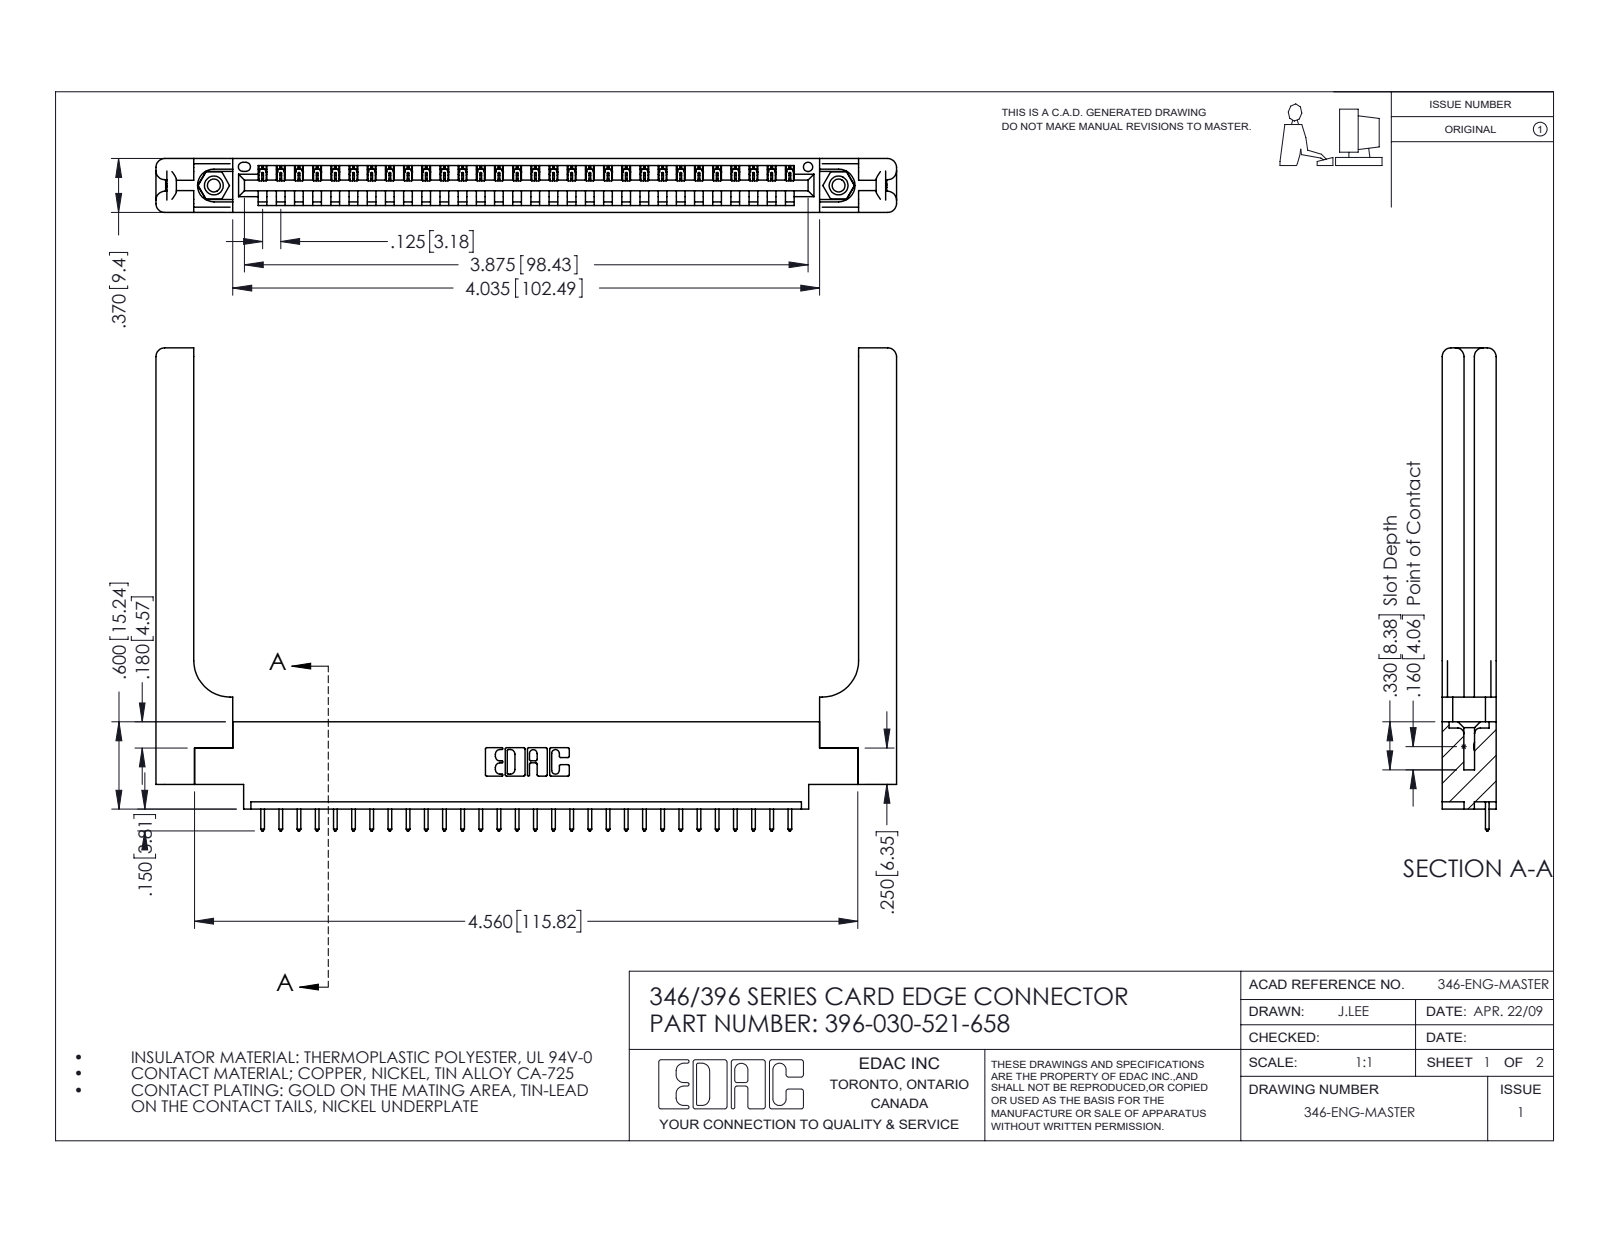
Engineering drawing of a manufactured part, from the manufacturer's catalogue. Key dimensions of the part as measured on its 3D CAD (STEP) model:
Part name (STEP PRODUCT): 345-250-001_345-250-001-102; 346-220-058_345-220-058; 345-292-001_345-293-121; 396-030-521-658 (+1 more)
STEP written by: SolidWorks 2016 (CONFIG_CONTROL_DESIGN)
Units: inches
Bodies: 35 solids, 2122 faces (1428 planar, 634 cylindrical, 60 other)
Overall size (bounding box): 5.091 × 3.32 × 0.37
Volume: 1.194 in³ · Surface area: 30.89 in²
Round holes (diameter × count): ⌀0.089 ×2, ⌀0.125 ×2, ⌀0.156 ×2, ⌀0.064 ×1
Round bosses / shafts (diameter × count): ⌀0.155 ×2
Partial cylindrical surfaces — rounded edges, fillets, slot ends (radius × count): R0.006 ×60, R0.01 ×60, R0.01 ×22, R0.06 ×16, R0.007 ×6, R0.031 ×6, R0.026 ×3, R0.03 ×2
Main face-to-face distances: 0.37, 0.072, 0.048, 0.322, 0.148, 0.15, 0.25, 0.298, 0.025, 0.076
Hole centre spacings: 0.246, 4.087, 4.295
